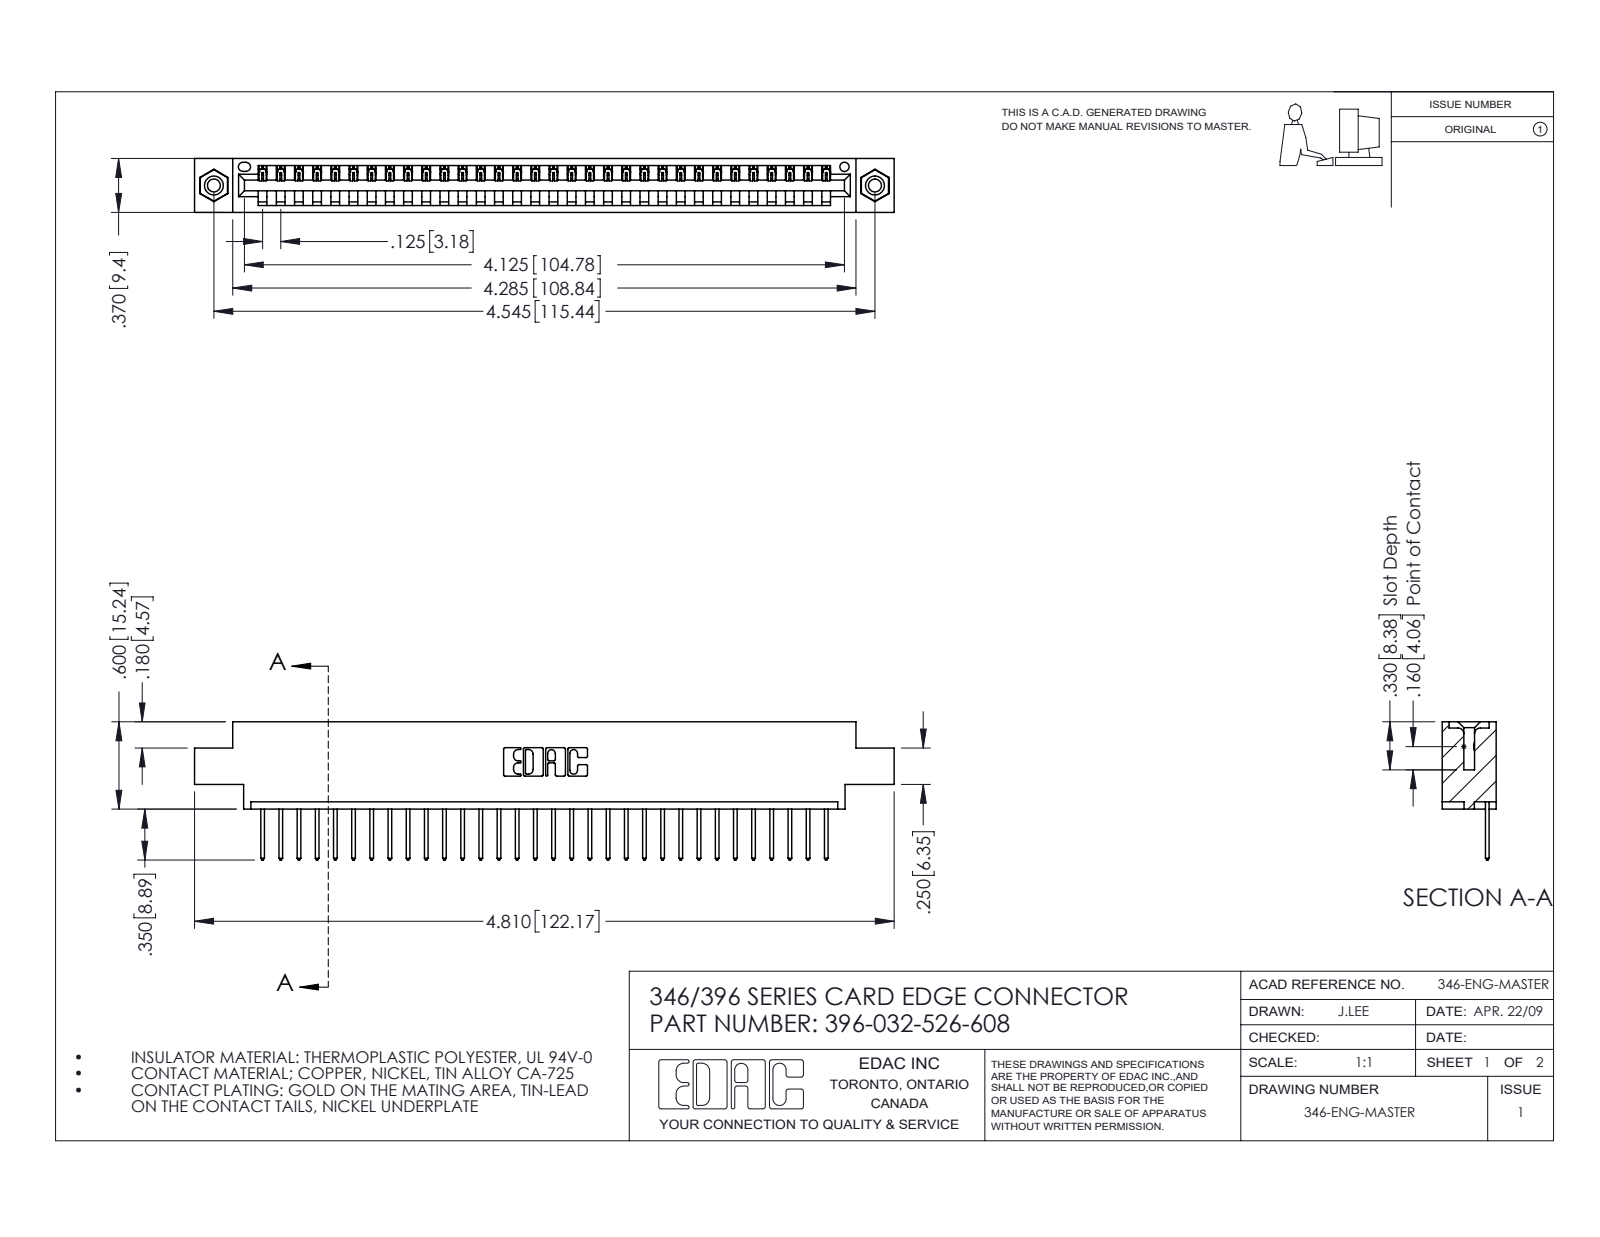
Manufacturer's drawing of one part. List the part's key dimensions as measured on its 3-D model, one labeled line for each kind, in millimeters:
Part name (STEP PRODUCT): 345-250-001_345-250-003-102; 396-032-526-608; 345-292-001_345-293-126; 346 Part_0.170 Offset - 0.156 Dia-TI
STEP written by: SolidWorks 2016 (CONFIG_CONTROL_DESIGN)
Units: millimetres
Bodies: 35 solids, 2042 faces (1392 planar, 634 cylindrical, 16 other)
Overall size (bounding box): 122.2 × 24.1 × 9.4
Volume: 11 400 mm³ · Surface area: 14 340 mm²
Round holes (diameter × count): ⌀2.3 ×2, ⌀3.2 ×2, ⌀4 ×2, ⌀1.6 ×1
Round bosses / shafts (diameter × count): ⌀3.9 ×2
Partial cylindrical surfaces — rounded edges, fillets, slot ends (radius × count): R0.2 ×64, R0.3 ×64, R0.3 ×22, R0.2 ×6, R0.8 ×6, R0.7 ×3, R0.8 ×2, R1 ×2
Main face-to-face distances: 1.2, 8.2, 9.4, 6.4, 1.8, 7.6, 0.6, 5.6, 3.8, 2.5
Hole centre spacings: 6.2, 110.2, 115.4
